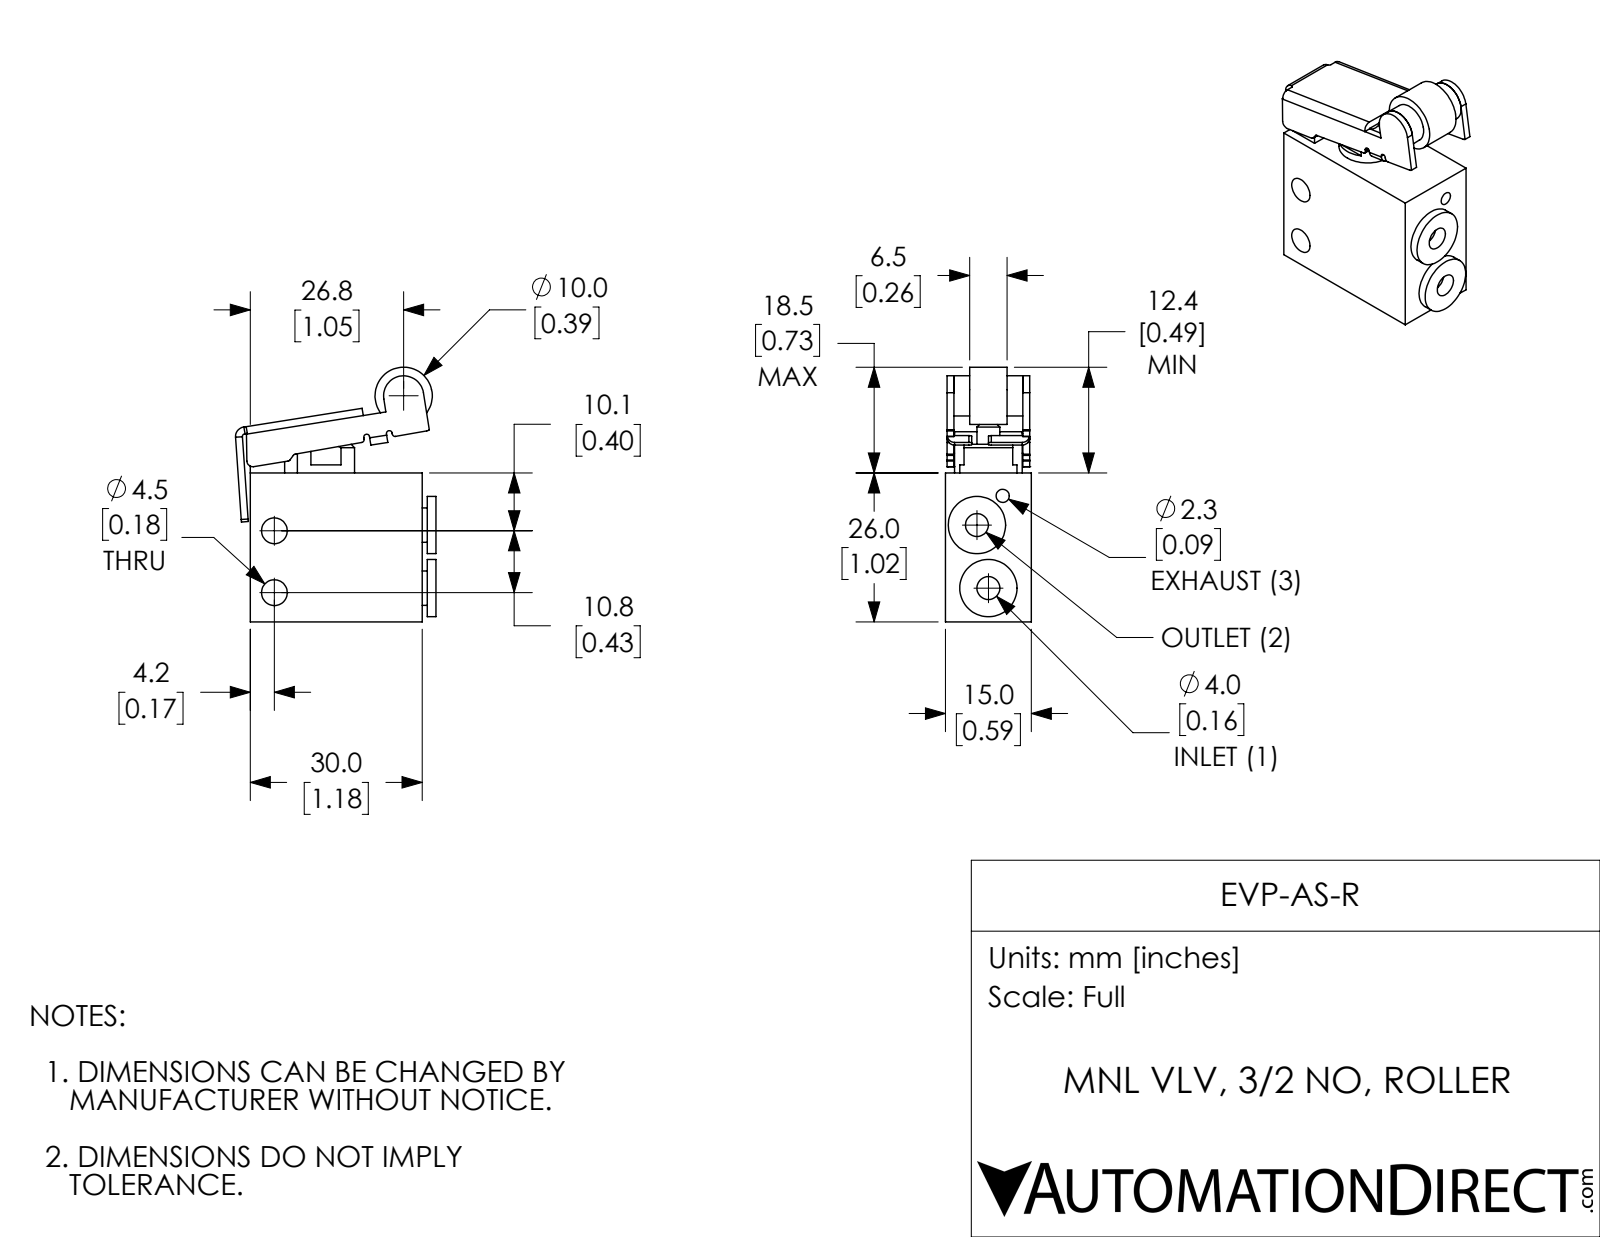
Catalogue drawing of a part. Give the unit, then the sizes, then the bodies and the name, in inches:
Units: inches
Overall size (bounding box): 1.75 × 1.378 × 0.591
Round holes (diameter × count): ⌀0.157 ×3, ⌀0.177 ×2, ⌀0.091 ×1, ⌀0.122 ×1
Round bosses / shafts (diameter × count): ⌀0.394 ×4, ⌀0.236 ×2, ⌀0.276 ×1, ⌀0.197 ×1, ⌀0.157 ×1
Partial cylindrical surfaces — rounded edges, fillets, slot ends (radius × count): R0.02 ×13, R0.051 ×4, R0.004 ×2, R0.016 ×2, R0.039 ×2, R0.067 ×1
Main face-to-face distances: 0.591, 0.047, 0.059, 0.531, 0.579, 0.52, 1.181, 1.024, 0.048, 0.472
Hole centre spacings: 0.268, 0.425, 0.44, 0.597, 0.641, 1.021
Volume: 0.871 in³ · Surface area: 11.21 in²
Bodies: 3 solids, 149 faces (75 planar, 70 cylindrical, 4 other)
Part name (STEP PRODUCT): EVP-AS-R
STEP written by: SolidWorks 2017 (AUTOMOTIVE_DESIGN)
